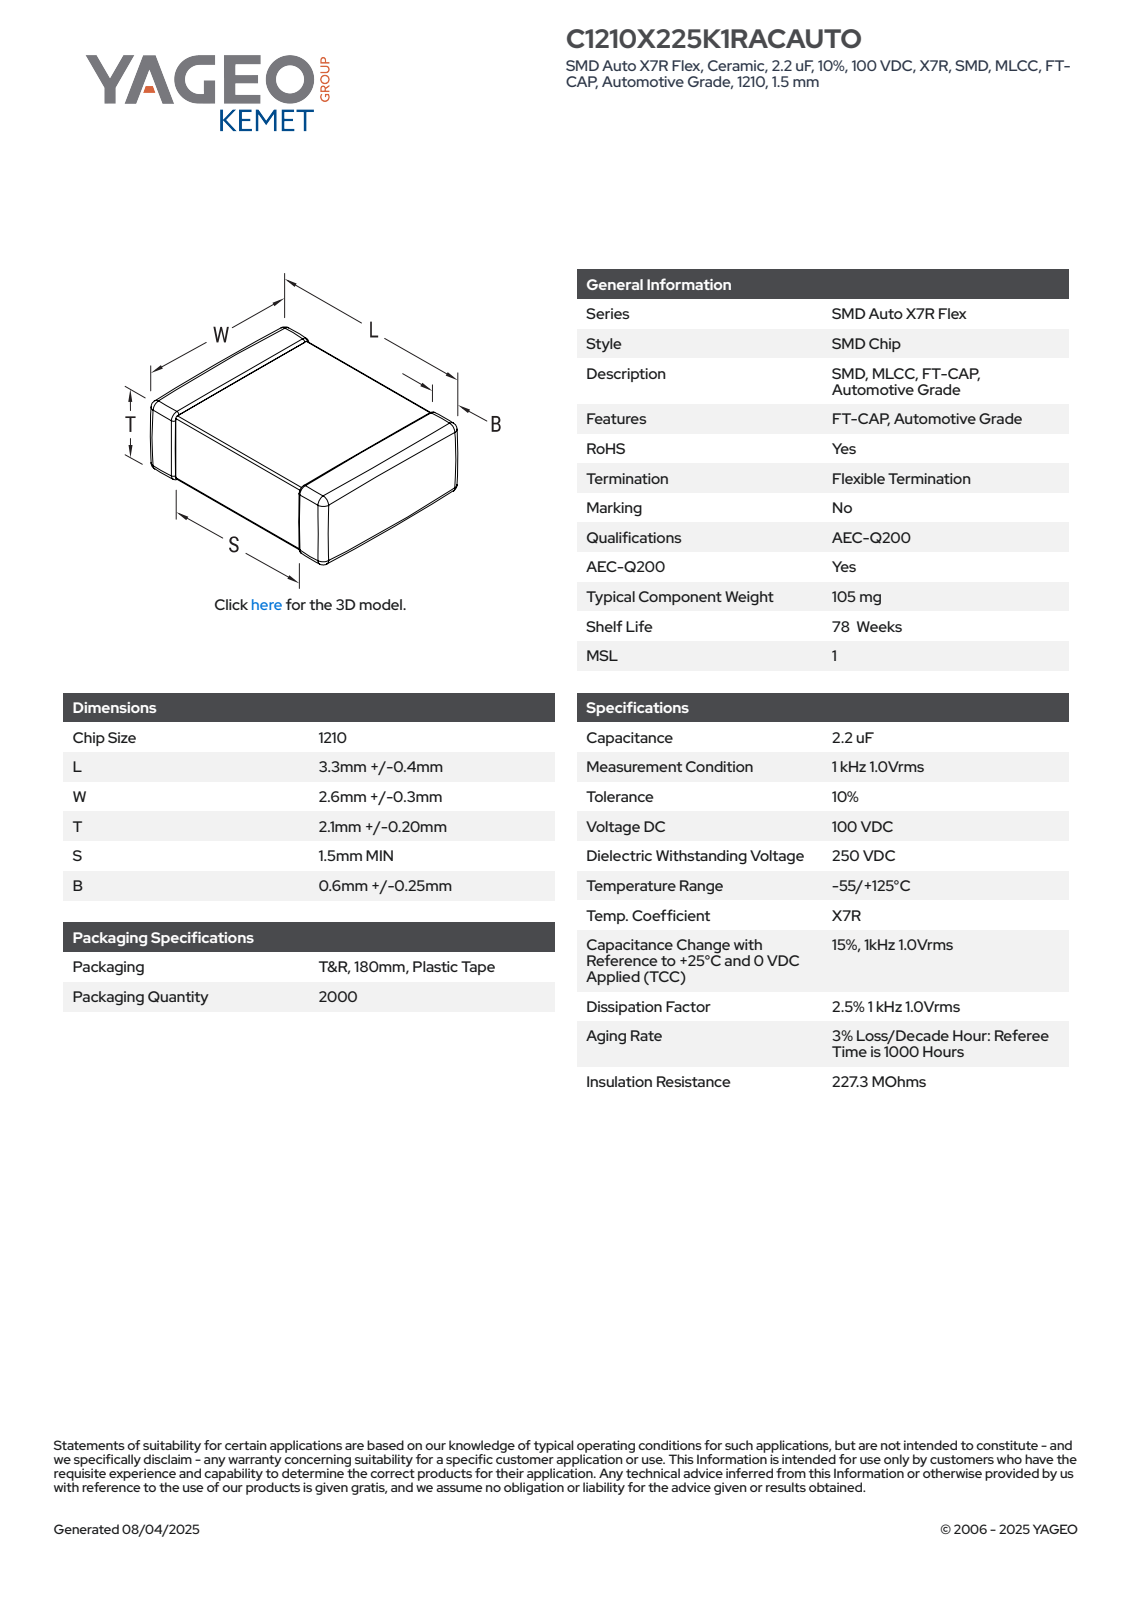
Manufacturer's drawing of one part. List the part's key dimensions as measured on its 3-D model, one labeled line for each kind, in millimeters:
Part name (STEP PRODUCT): CCS_CCSTDNOS_1210_L3.7W2.9T2.3B0.85
STEP written by: SolidWorks 2014 (AUTOMOTIVE_DESIGN)
Units: millimetres
Bodies: 4 solids, 125 faces (71 planar, 38 cylindrical, 16 other)
Overall size (bounding box): 3.7 × 2.9 × 2.3
Volume: 23 mm³ · Surface area: 51 mm²
Main face-to-face distances: 2.24, 2.84, 3.7, 2.18, 2.78, 2.3, 2.9, 1.4, 1.5, 1.34
